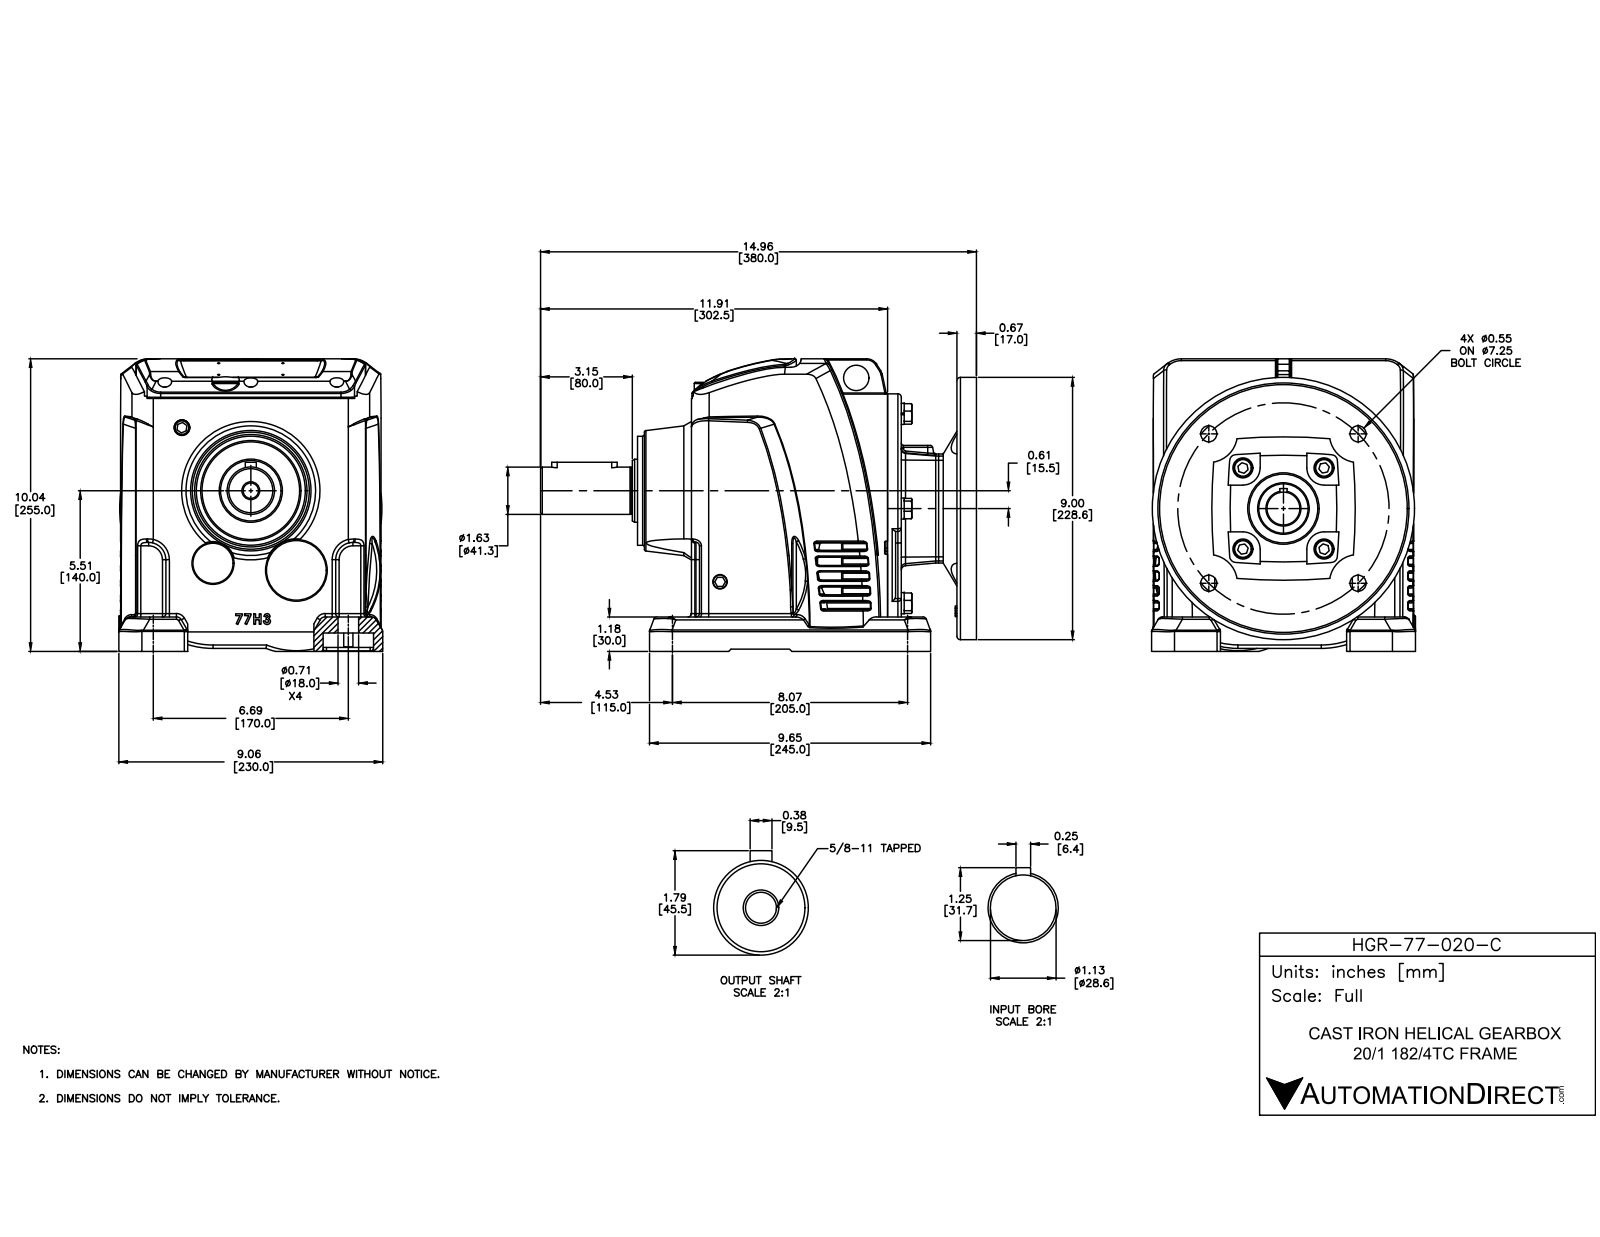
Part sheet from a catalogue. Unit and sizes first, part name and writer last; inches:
Units: inches
Overall size (bounding box): 14.961 × 10.039 × 9.055
Round holes (diameter × count): ⌀0.472 ×6, ⌀0.079 ×4, ⌀0.551 ×4, ⌀0.689 ×4, ⌀0.709 ×4, ⌀0.531 ×1, ⌀0.866 ×1, ⌀0.945 ×1, ⌀1.126 ×1, ⌀1.772 ×1, ⌀2.165 ×1, ⌀8.5 ×1
Round bosses / shafts (diameter × count): ⌀0.512 ×5, ⌀0.724 ×4, ⌀0.63 ×4, ⌀0.394 ×3, ⌀9 ×1, ⌀7.874 ×1, ⌀3.74 ×1, ⌀3.346 ×1
Partial cylindrical surfaces — rounded edges, fillets, slot ends (radius × count): R0.118 ×49, R0.039 ×33, R0.591 ×8, R0.079 ×4, R0.197 ×4, R0.315 ×4, R0.394 ×4, R0.689 ×4
Main face-to-face distances: 0.039, 6.732, 2.851, 0.469, 2.382, 9.583, 9.114, 8.583, 0.472, 1.909
Hole centre spacings: 4.125, 1.656, 1.969, 2.784, 3.625, 5.127, 5.594, 6.693
Volume: 579.4 in³ · Surface area: 1 019 in²
Bodies: 30 solids, 1179 faces (369 planar, 298 cylindrical, 512 other)
Part name (STEP PRODUCT): HGR-77-005-C
STEP written by: SolidWorks 2015 (CONFIG_CONTROL_DESIGN)
